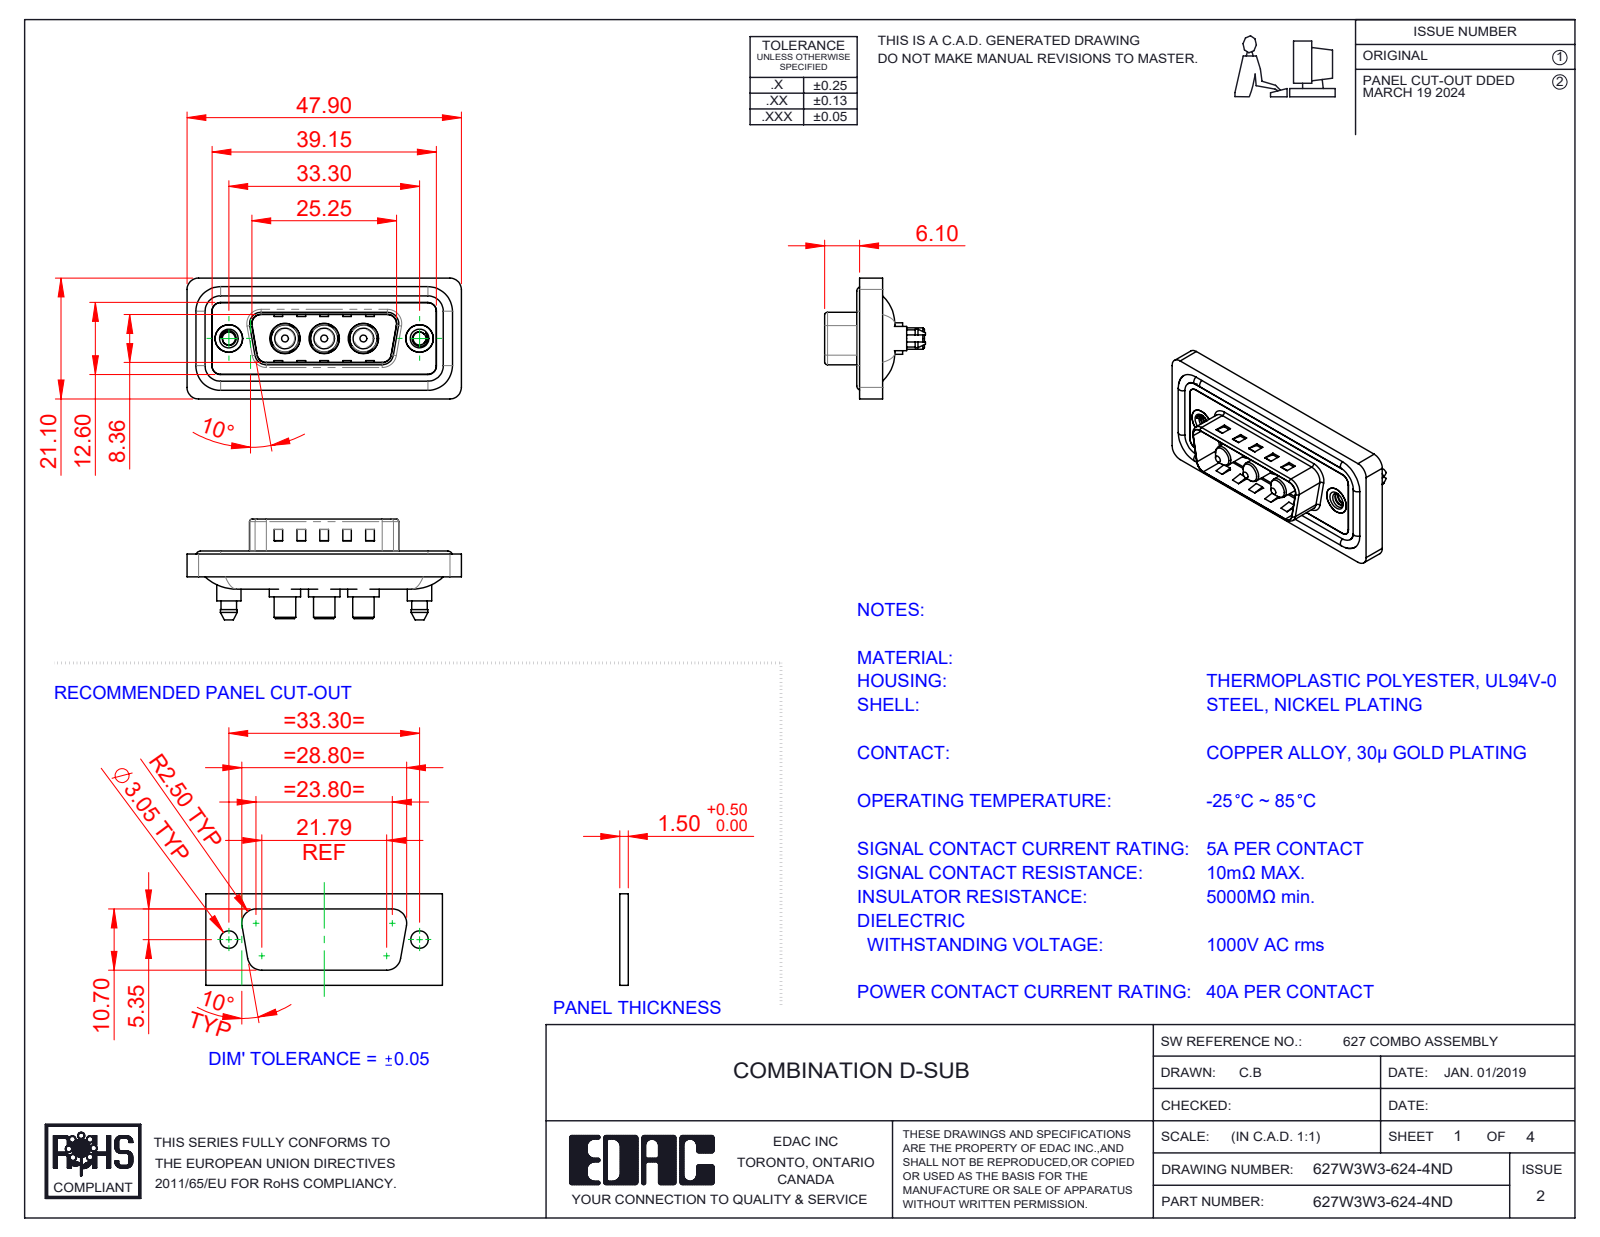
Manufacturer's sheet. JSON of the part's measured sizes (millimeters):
{"part_name": "627Combo Shell Front_15 Contacts; 627Combo Housing_3W3; 627Combo Shell Rear_15 Contacts; 627Combo Threaded Boardlock_D (+4 more)", "step_written_by": "SolidWorks 2023 (CONFIG_CONTROL_DESIGN)", "units": "millimeters", "bodies": {"solids": 13, "faces": 622, "planar": 223, "cylindrical": 281, "other": 118}, "overall_size": [47.9, 21.1, 17.6], "volume_mm3": 5776, "surface_area_mm2": 9122, "round_holes": [[4.85, 3], [5.3, 3], [2.26, 2], [4, 2], [4.8, 2], [5, 2]], "round_bosses_or_shafts": [[1.6, 4], [5.5, 3], [5.2, 3], [4.75, 3], [3.75, 3], [3.6, 3], [5.4, 2], [4.9, 2]], "partial_cylinders_radius": [[1.5, 28], [2, 20], [1.6, 10], [0.5, 8], [0.25, 4], [0.6, 4], [0.65, 4], [0.9, 4]], "face_to_face_distances": [0.4, 1.1, 3.1, 1.5, 1.6, 0.5, 2.9, 4, 0.7, 0.82], "hole_center_spacings": [6.85, 9.8, 16.65, 23.5, 13.7, 33.3]}
